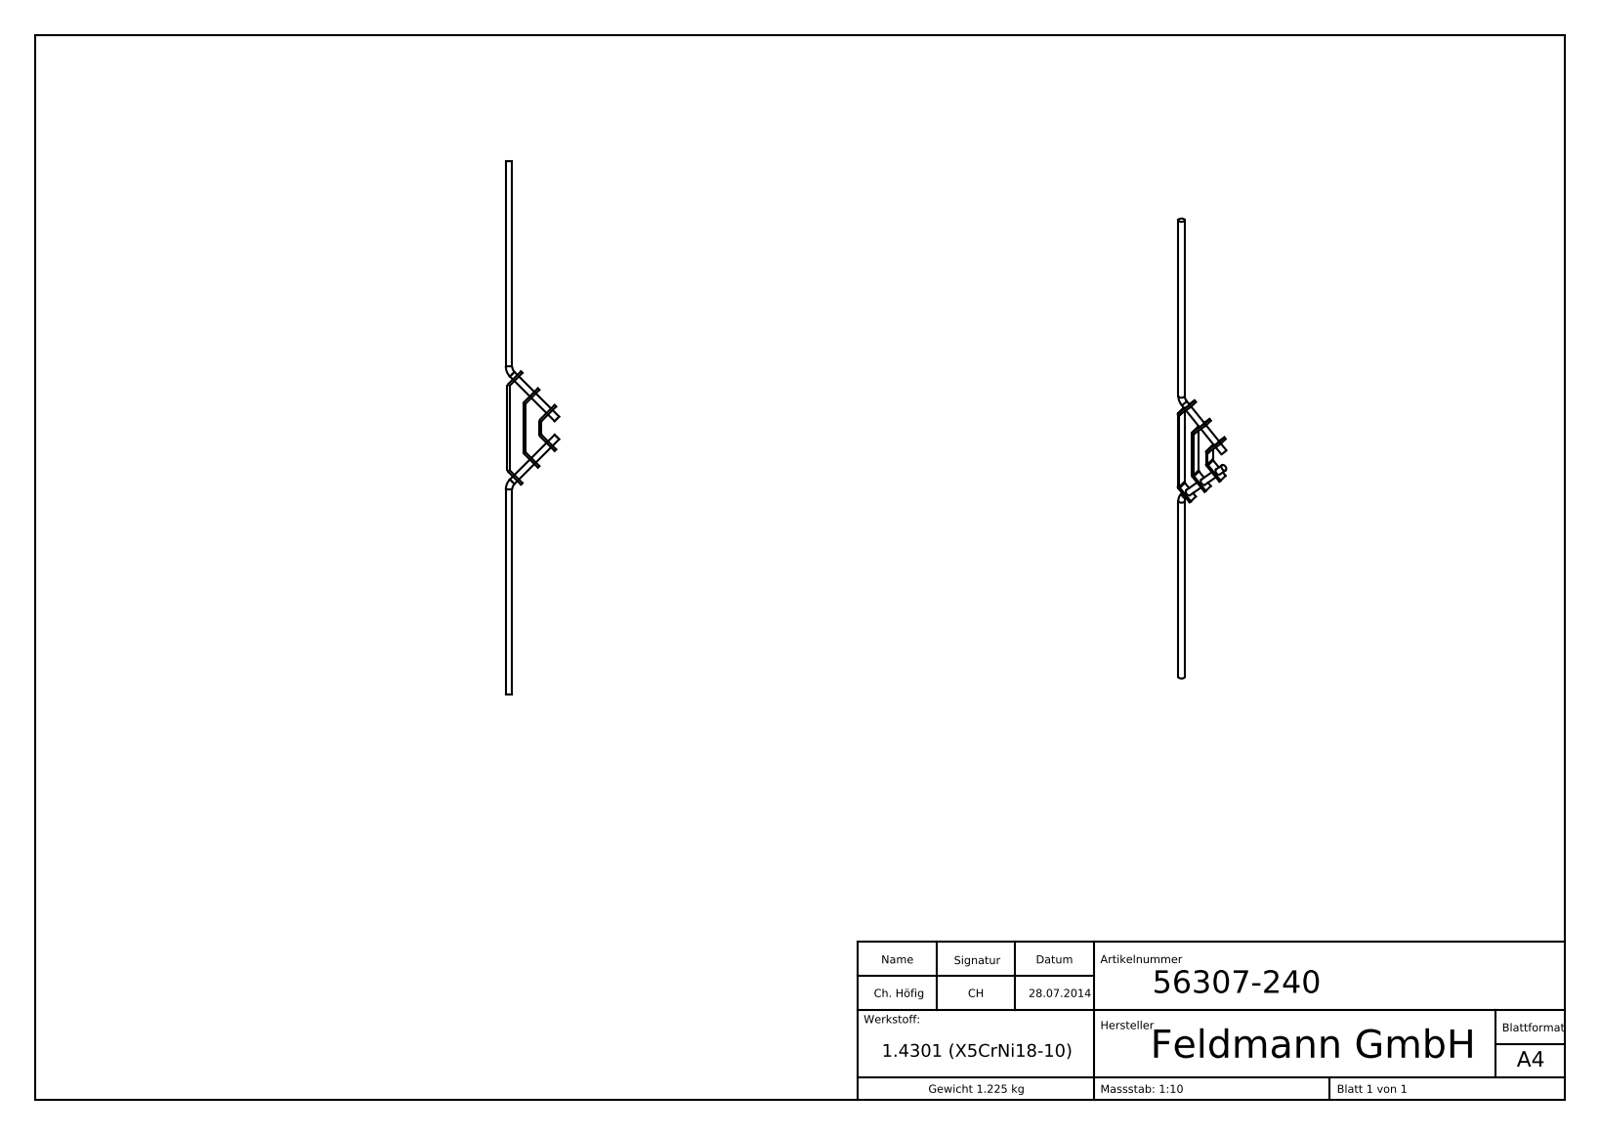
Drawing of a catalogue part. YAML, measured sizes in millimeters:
part_name: "56307-240"
step_written_by: "SolidWorks 2015 (CONFIG_CONTROL_DESIGN)"
units: millimeters
bodies: {solids: 1, faces: 183, planar: 99, cylindrical: 32, other: 52}
overall_size: [1000, 100, 20]
volume: 155025
surface_area: 62000
round_bosses_or_shafts:
  - {diameter: 12, count: 3}
partial_cylinders:
  - {radius: 3, count: 6}
  - {radius: 6, count: 6}
face_to_face_distances: [4, 30, 44.3, 26, 34, 20, 48.3, 40.3, 44.99, 89.29]
